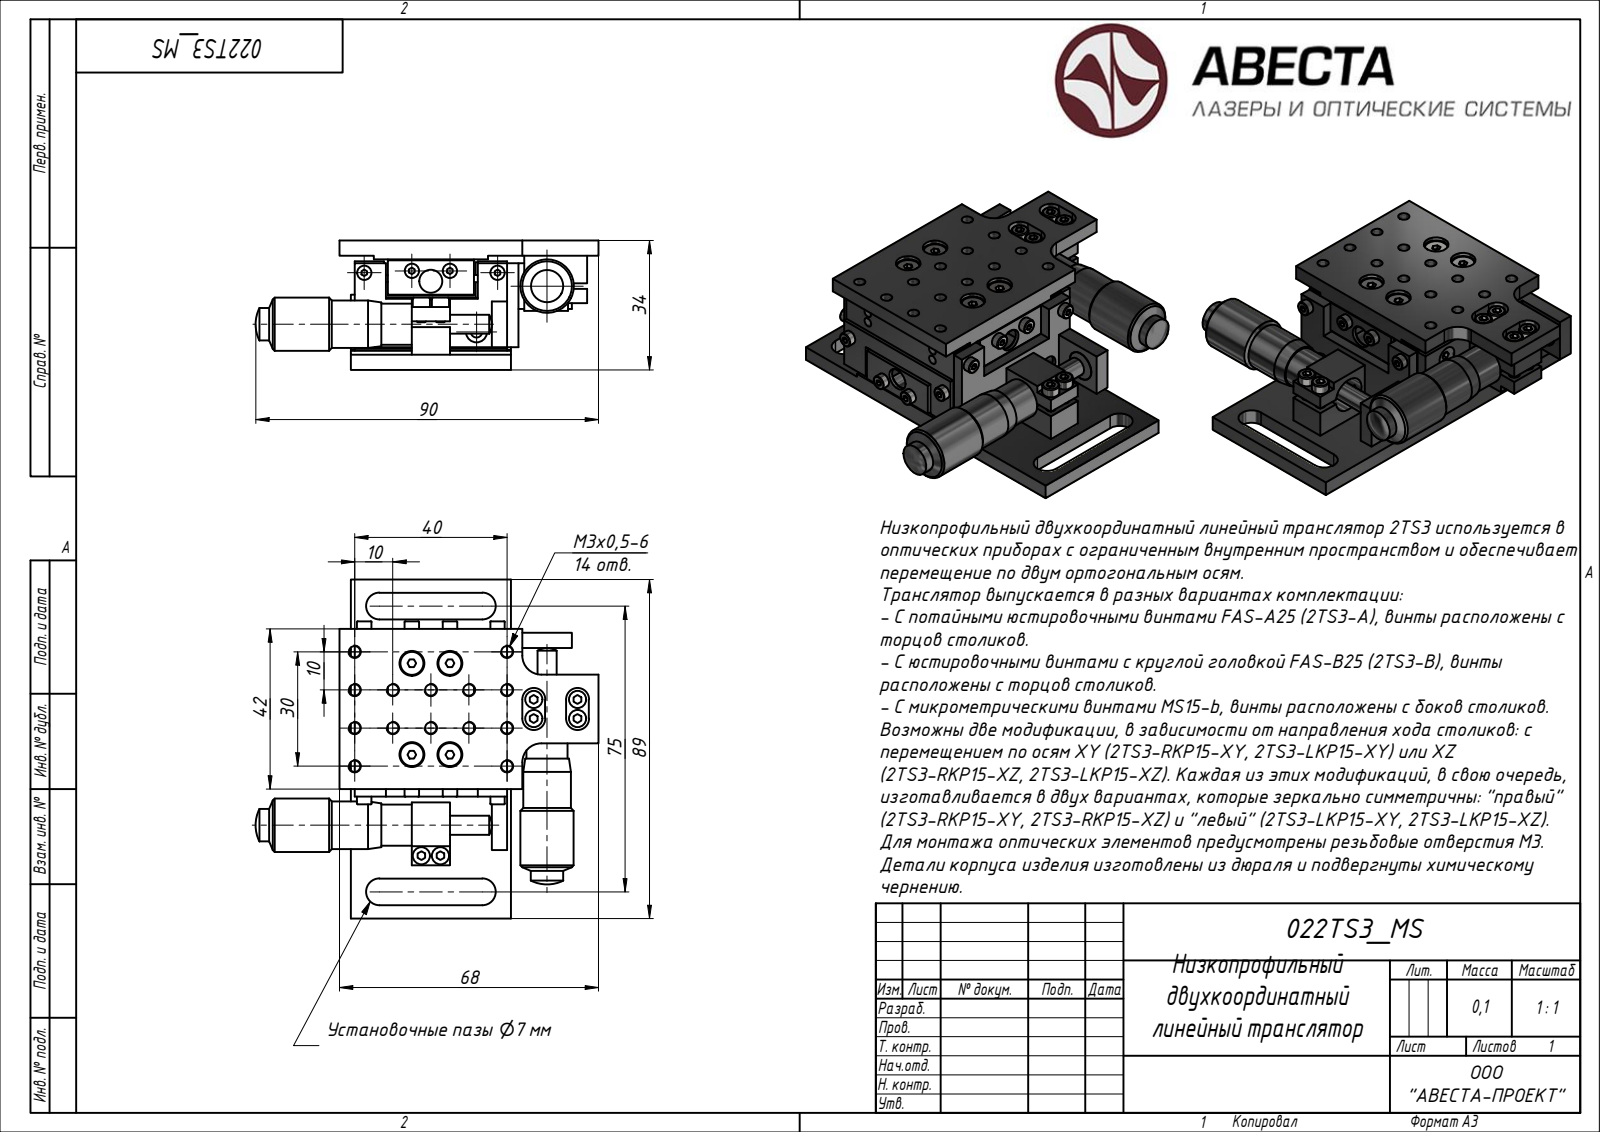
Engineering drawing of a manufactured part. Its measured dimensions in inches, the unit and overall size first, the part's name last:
Units: inches
Overall size (bounding box): 3.543 × 3.504 × 1.339
Bodies: 30 solids, 1192 faces (0 planar, 0 cylindrical, 1192 other)
STEP written by: ST-DEVELOPER v15 (AUTOMOTIVE_DESIGN)
